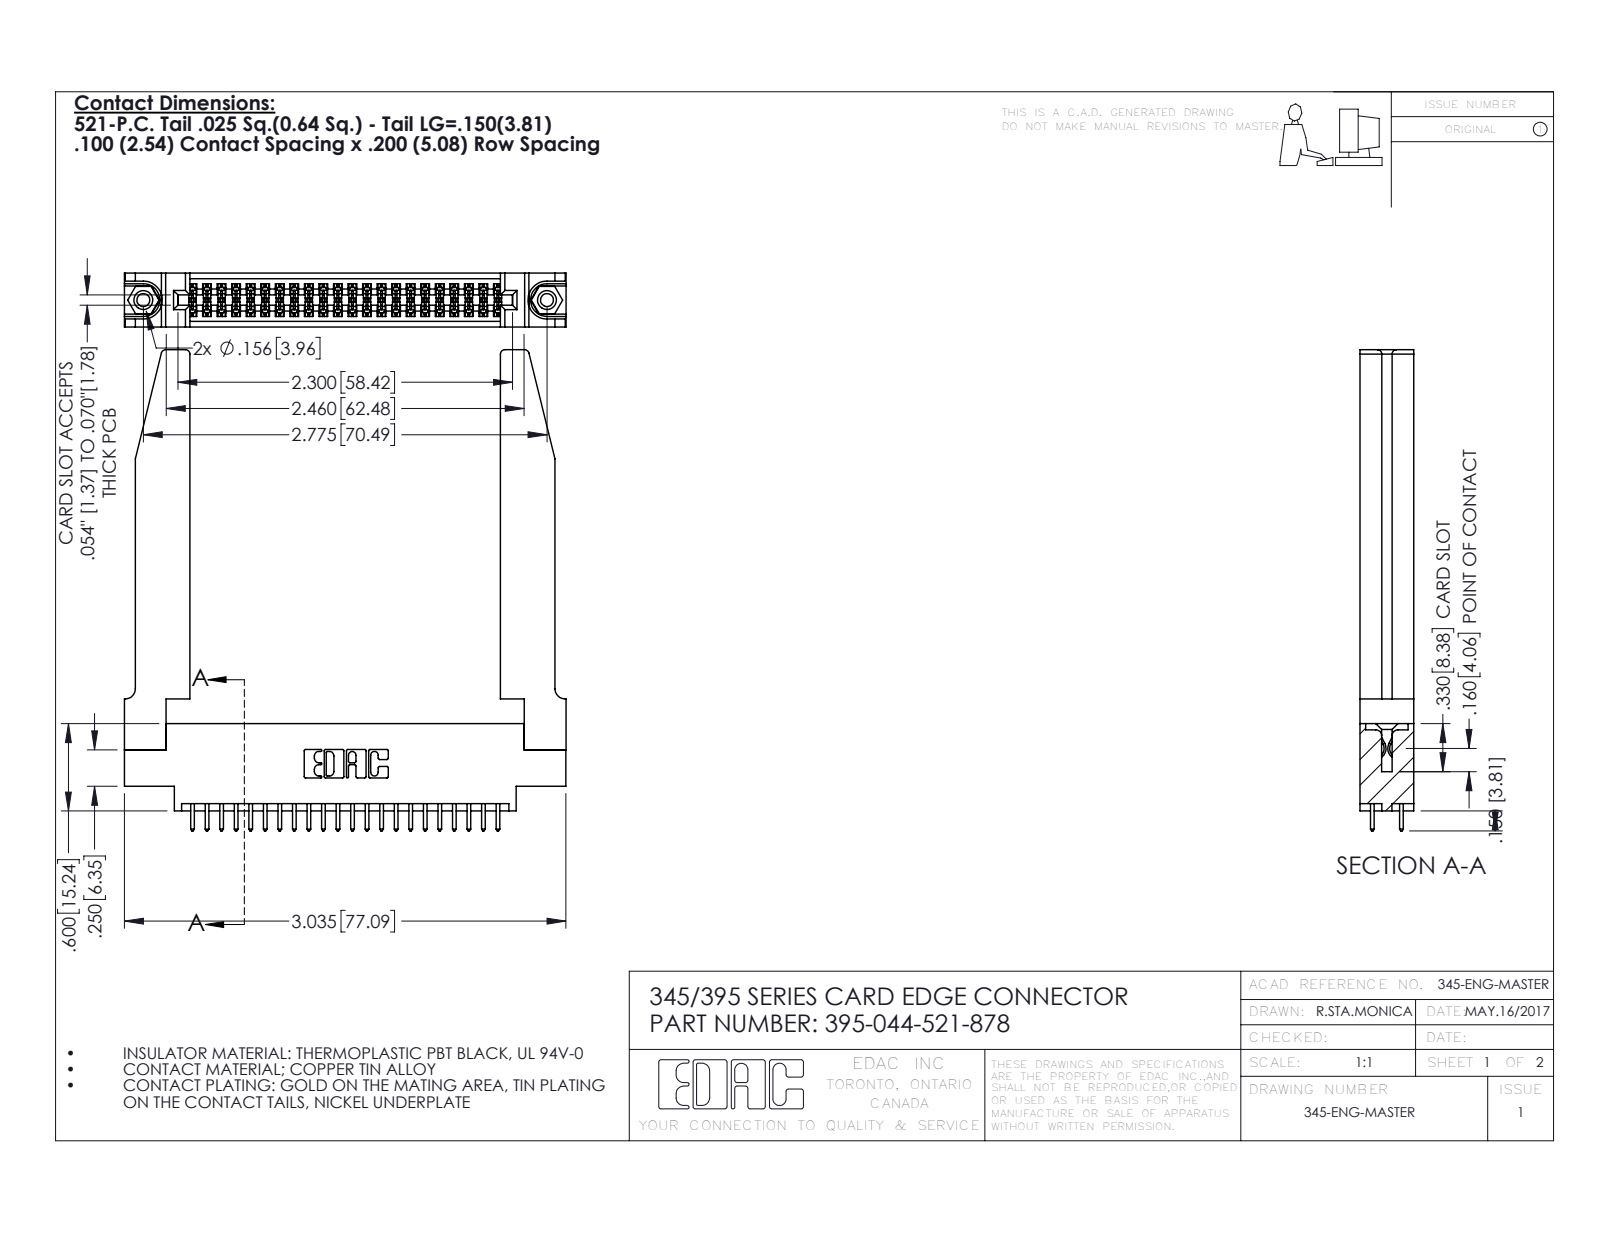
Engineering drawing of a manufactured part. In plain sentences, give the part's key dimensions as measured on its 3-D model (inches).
The part is named "395-044-521-878; 345-292-001_345-293-121; 345 Part_0.170 Offset - 0.156 Dia-TH; 345-220-078_345-220-078 (+1 more)". Its 3-D file was written by "SolidWorks 2016 (CONFIG_CONTROL_DESIGN)". It is 49 solids with 2564 faces: 1678 planar, 834 cylindrical and 52 other. Overall it measures 3.307 by 3.036 by 0.37 inches. Its volume is 0.912 cubic inches and its surface area 26.48 square inches. Round holes: 2 of diameter 0.089, 2 of diameter 0.125, 2 of diameter 0.156, 1 of diameter 0.064. Round bosses or shafts: 2 of diameter 0.155. Partial cylindrical surfaces (rounded edges, fillets, slot ends): 66 of radius 0.006, 44 of radius 0.01, 22 of radius 0.01, 8 of radius 0.03, 6 of radius 0.007, 6 of radius 0.031, 3 of radius 0.026, 2 of radius 0.014. The main face-to-face distances are 0.37, 0.072, 0.298, 0.098, 0.272, 0.025, 0.2, 0.225, 0.148, 0.15. The hole center spacings are 0.27, 2.541, 2.775.
